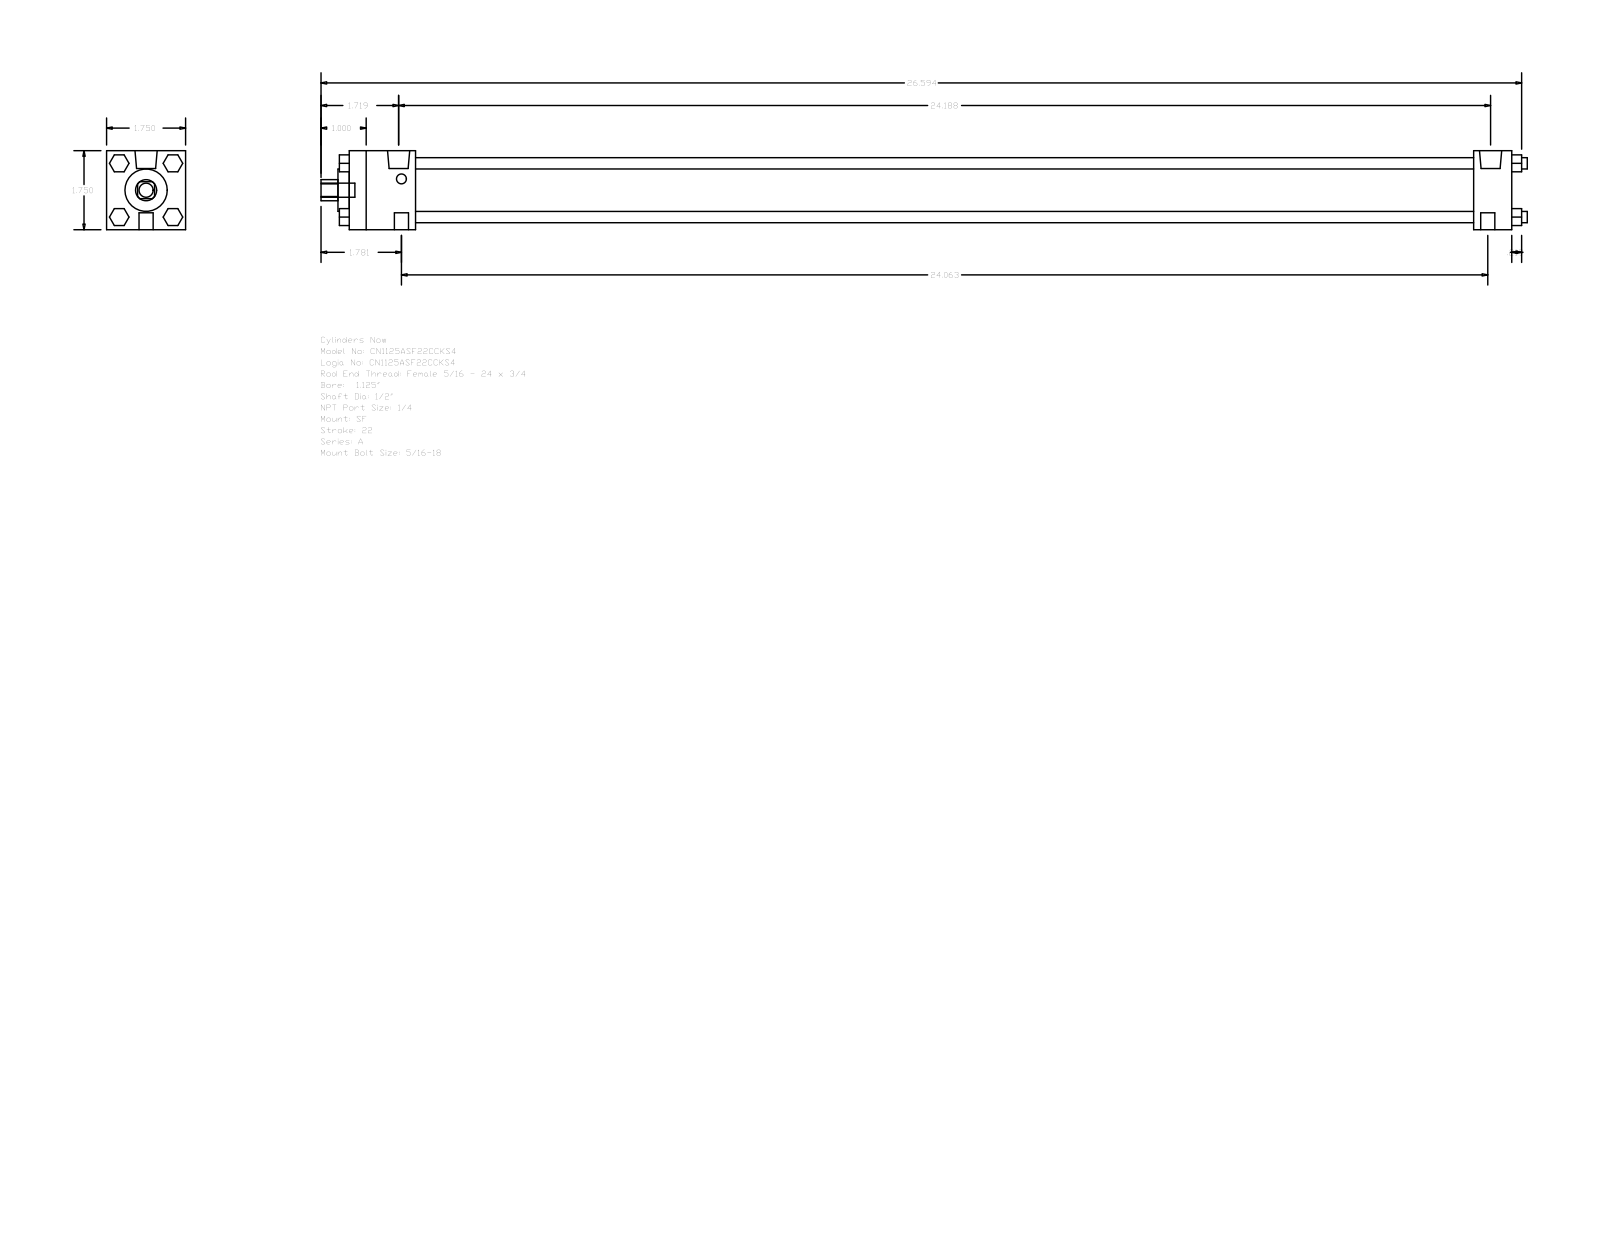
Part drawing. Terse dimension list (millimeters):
name: A_SF__0112_0.5
written by: GSSL Pune (CONFIG_CONTROL_DESIGN)
unit: mm
bodies: 0 solids, 120 faces (92 planar, 28 cylindrical, 0 other)
size: 678.66 × 44.45 × 44.45
holes: 1× ⌀12.7, 1× ⌀23.81, 1× ⌀31.88
bosses: 4× ⌀6.35, 3× ⌀7.94, 2× ⌀12.49, 2× ⌀5.56
rounds: 1× R5.94
face distances: 44.46, 654.04, 632.61, 21.43, 37.3, 595.31, 616.74, 9.53, 5.59, 9.52
